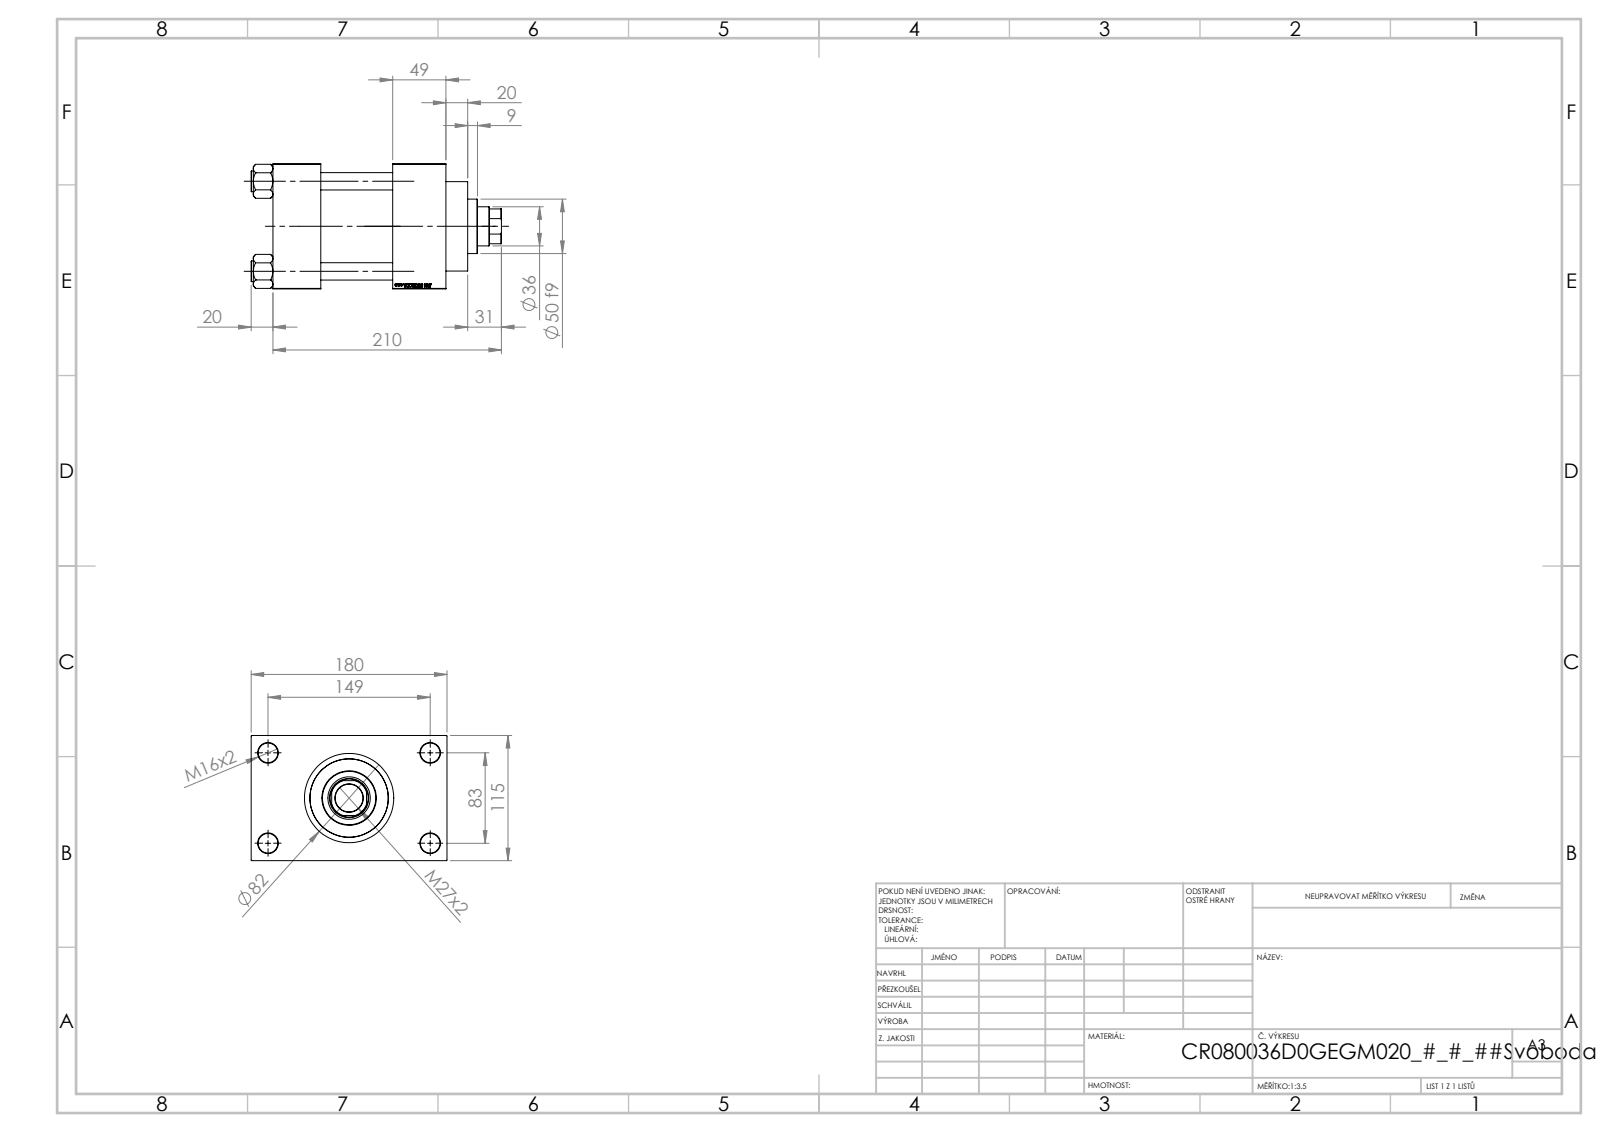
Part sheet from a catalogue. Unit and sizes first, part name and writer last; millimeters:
Units: millimetres
Overall size (bounding box): 230 × 180 × 115
Round holes (diameter × count): ⌀16 ×4, ⌀18 ×4, ⌀7 ×2, ⌀26.44 ×2, ⌀35 ×2, ⌀25.5 ×1, ⌀36 ×1, ⌀39 ×1, ⌀61 ×1, ⌀72 ×1, ⌀80 ×1
Round bosses / shafts (diameter × count): ⌀19 ×4, ⌀86 ×1, ⌀82 ×1, ⌀50 ×1
Partial cylindrical surfaces — rounded edges, fillets, slot ends (radius × count): R17.5 ×1
Main face-to-face distances: 115, 66, 110, 49, 44, 159, 32.5, 147.5, 20, 69
Hole centre spacings: 33.15, 58.48, 82.7, 85.28, 89.24, 115.85, 142.43, 83
Volume: 1 997 000 mm³ · Surface area: 293 897 mm²
Bodies: 11 solids, 1152 faces (545 planar, 89 cylindrical, 518 other)
Part name (STEP PRODUCT): V215CR_VCP_D; V215CR_D_Body; V215_VC_A; V215CR_D_TYCINKA (+1 more)
STEP written by: SolidWorks 2019 (CONFIG_CONTROL_DESIGN)
